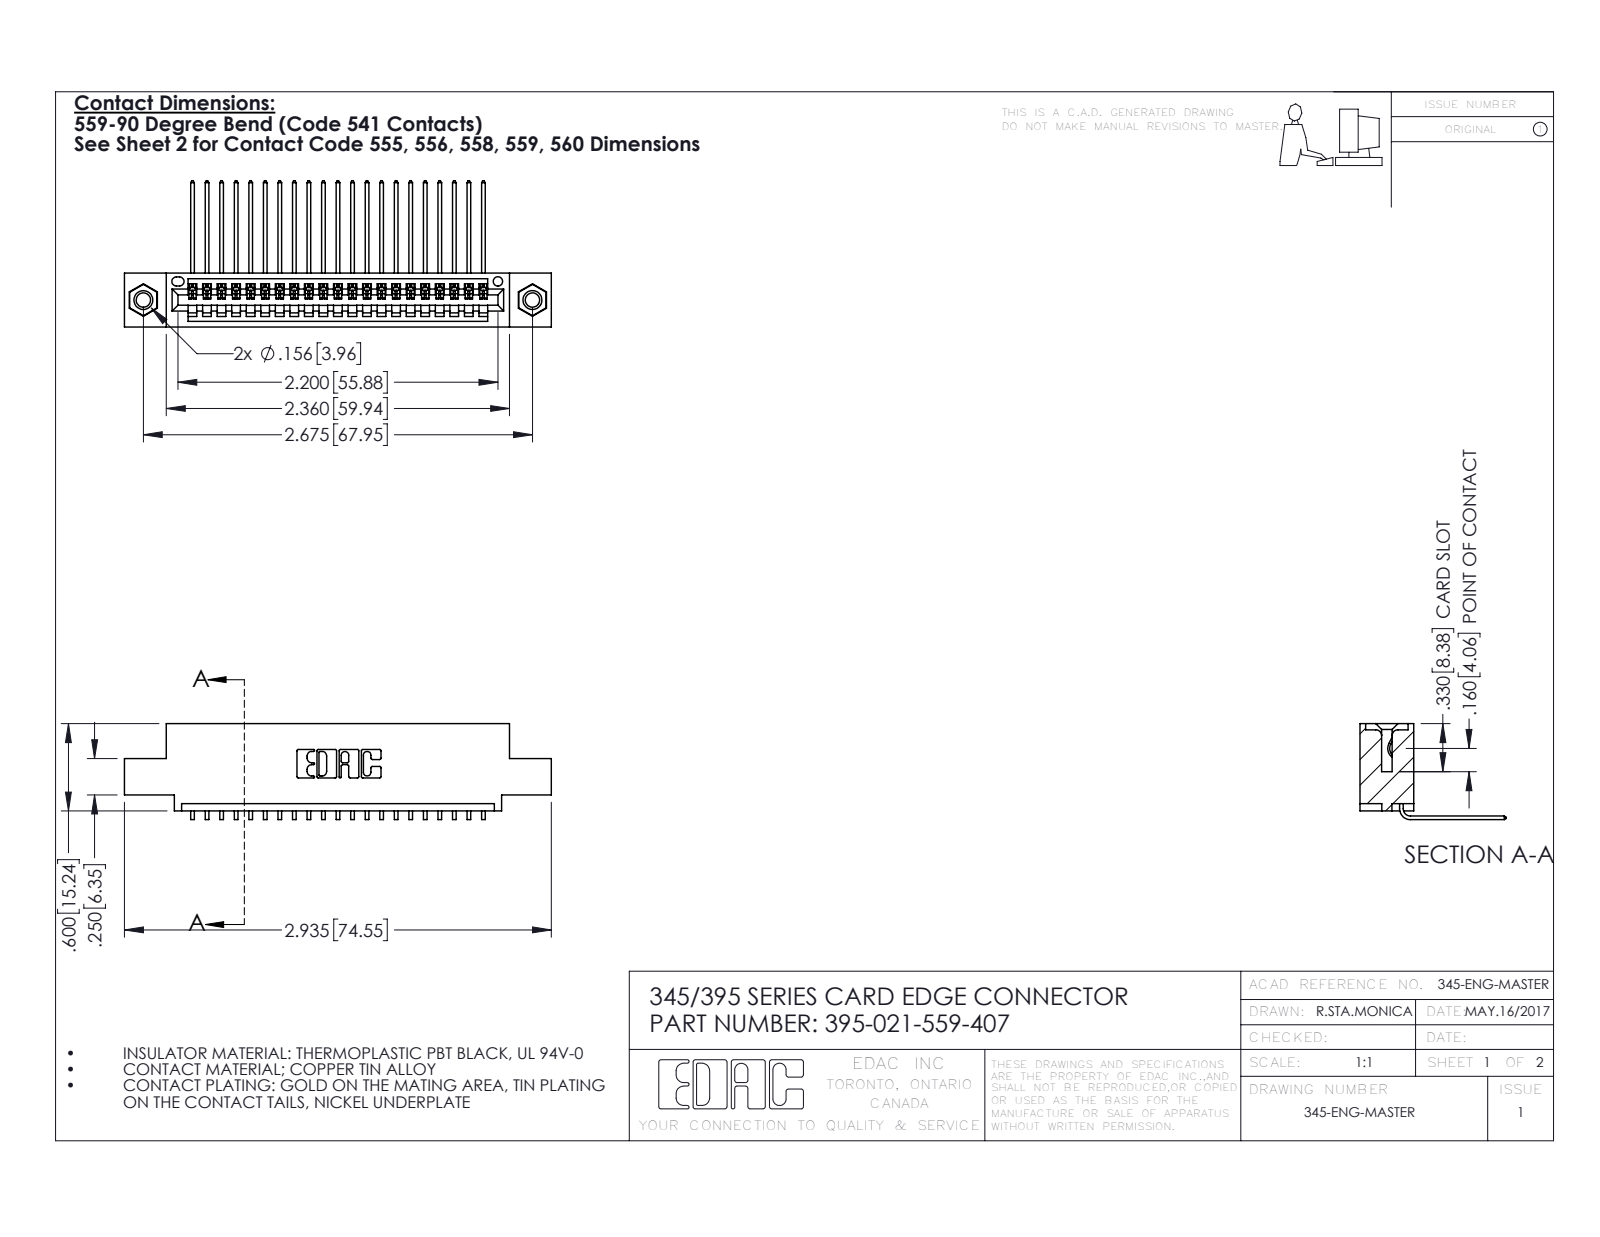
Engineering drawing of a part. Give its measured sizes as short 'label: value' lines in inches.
name: 345-292-001_558 559 Tail - 1; 345 Part_0.110 Offset - 0.156 Dia-TI; 345-250-001_345-250-005-103; 395-021-559-407
written by: SolidWorks 2016 (CONFIG_CONTROL_DESIGN)
unit: in
bodies: 24 solids, 1450 faces (998 planar, 436 cylindrical, 16 other)
size: 2.935 × 1.005 × 0.659
volume: 0.421 in³; area: 14.57 in²
holes: 2× ⌀0.098, 2× ⌀0.125, 2× ⌀0.156, 1× ⌀0.064
bosses: 2× ⌀0.155
rounds: 42× R0.006, 22× R0.01, 6× R0.007, 6× R0.031, 3× R0.026, 2× R0.031, 2× R0.04, 1× R0.014
face distances: 0.072, 0.298, 0.37, 0.2, 0.098, 0.272, 0.025, 0.225, 0.149, 0.072
hole spacings: 0.27, 2.441, 2.675
